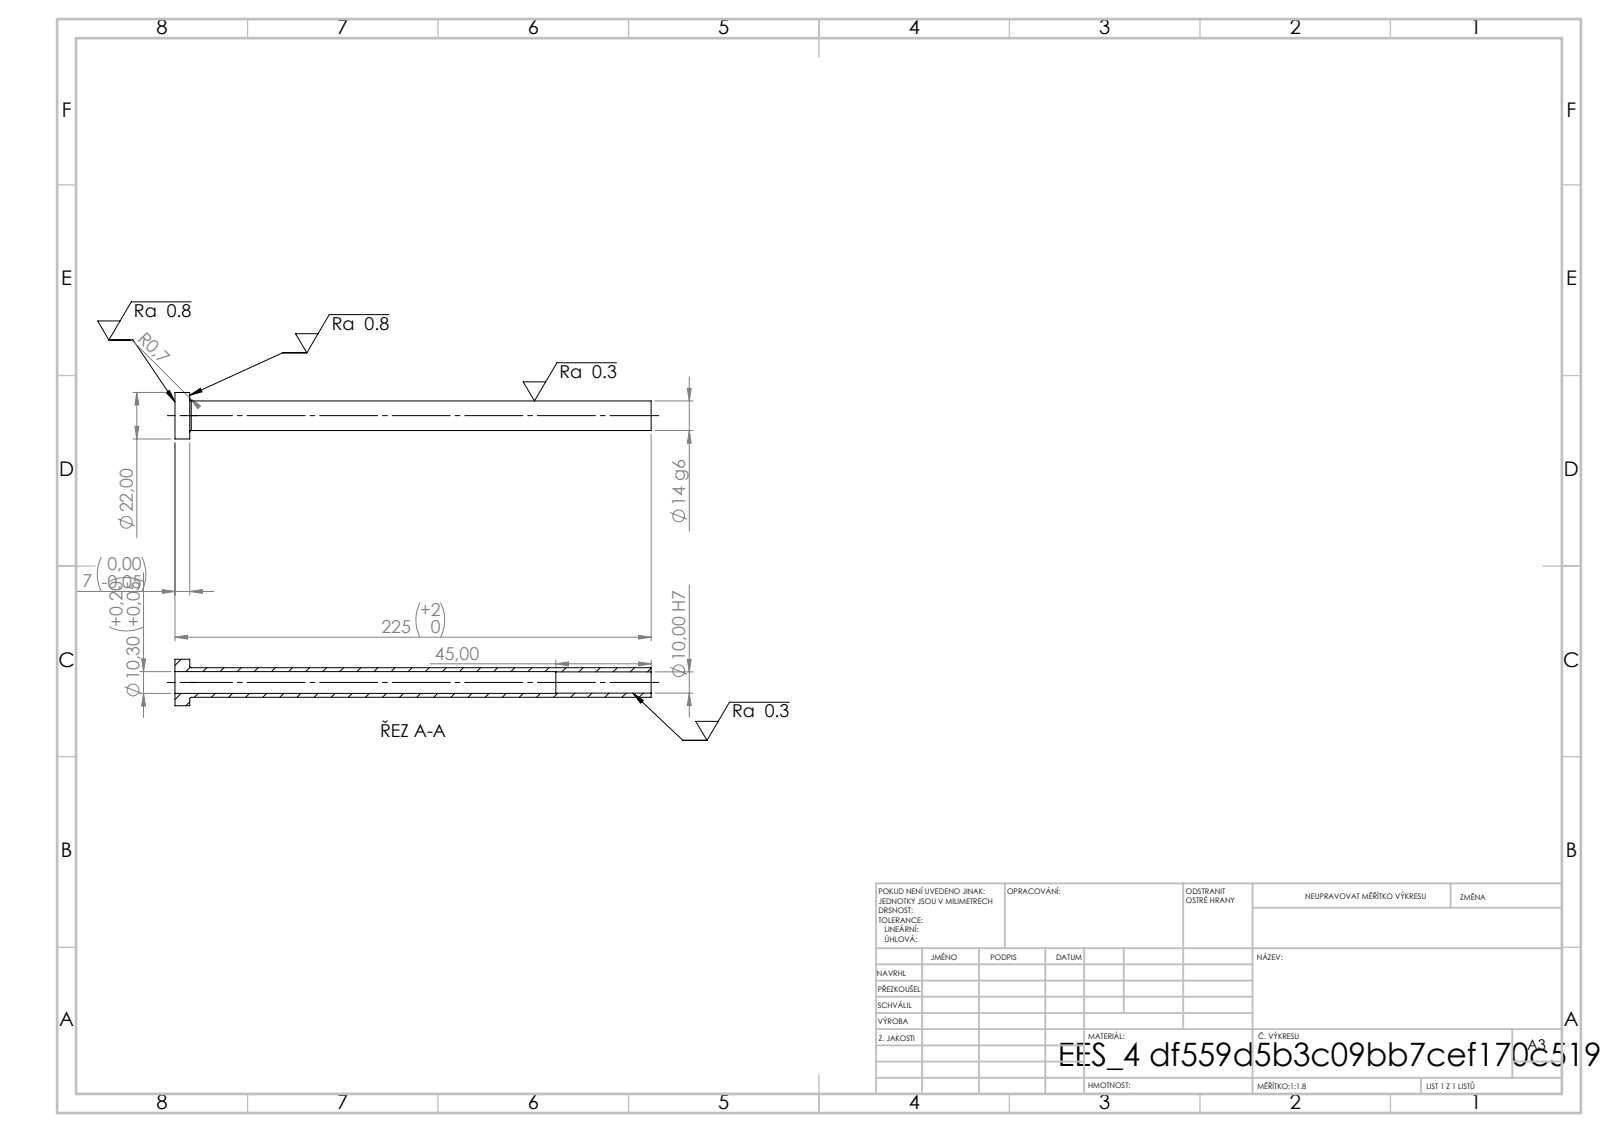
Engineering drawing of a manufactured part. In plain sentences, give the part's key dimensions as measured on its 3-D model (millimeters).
Its 3-D file was written by "SolidWorks 2019 (CONFIG_CONTROL_DESIGN)". It is 1 solid with 14 faces: 4 planar, 8 cylindrical and 2 other. Overall it measures 225 by 22 by 22 millimeters. Its volume is 17 692 cubic millimeters and its surface area 17 900 square millimeters. Round holes: 1 of diameter 10, 1 of diameter 10.3. Round bosses or shafts: 1 of diameter 22, 1 of diameter 14. The main face-to-face distances are 7, 225, 218, 180, 173, 45.
